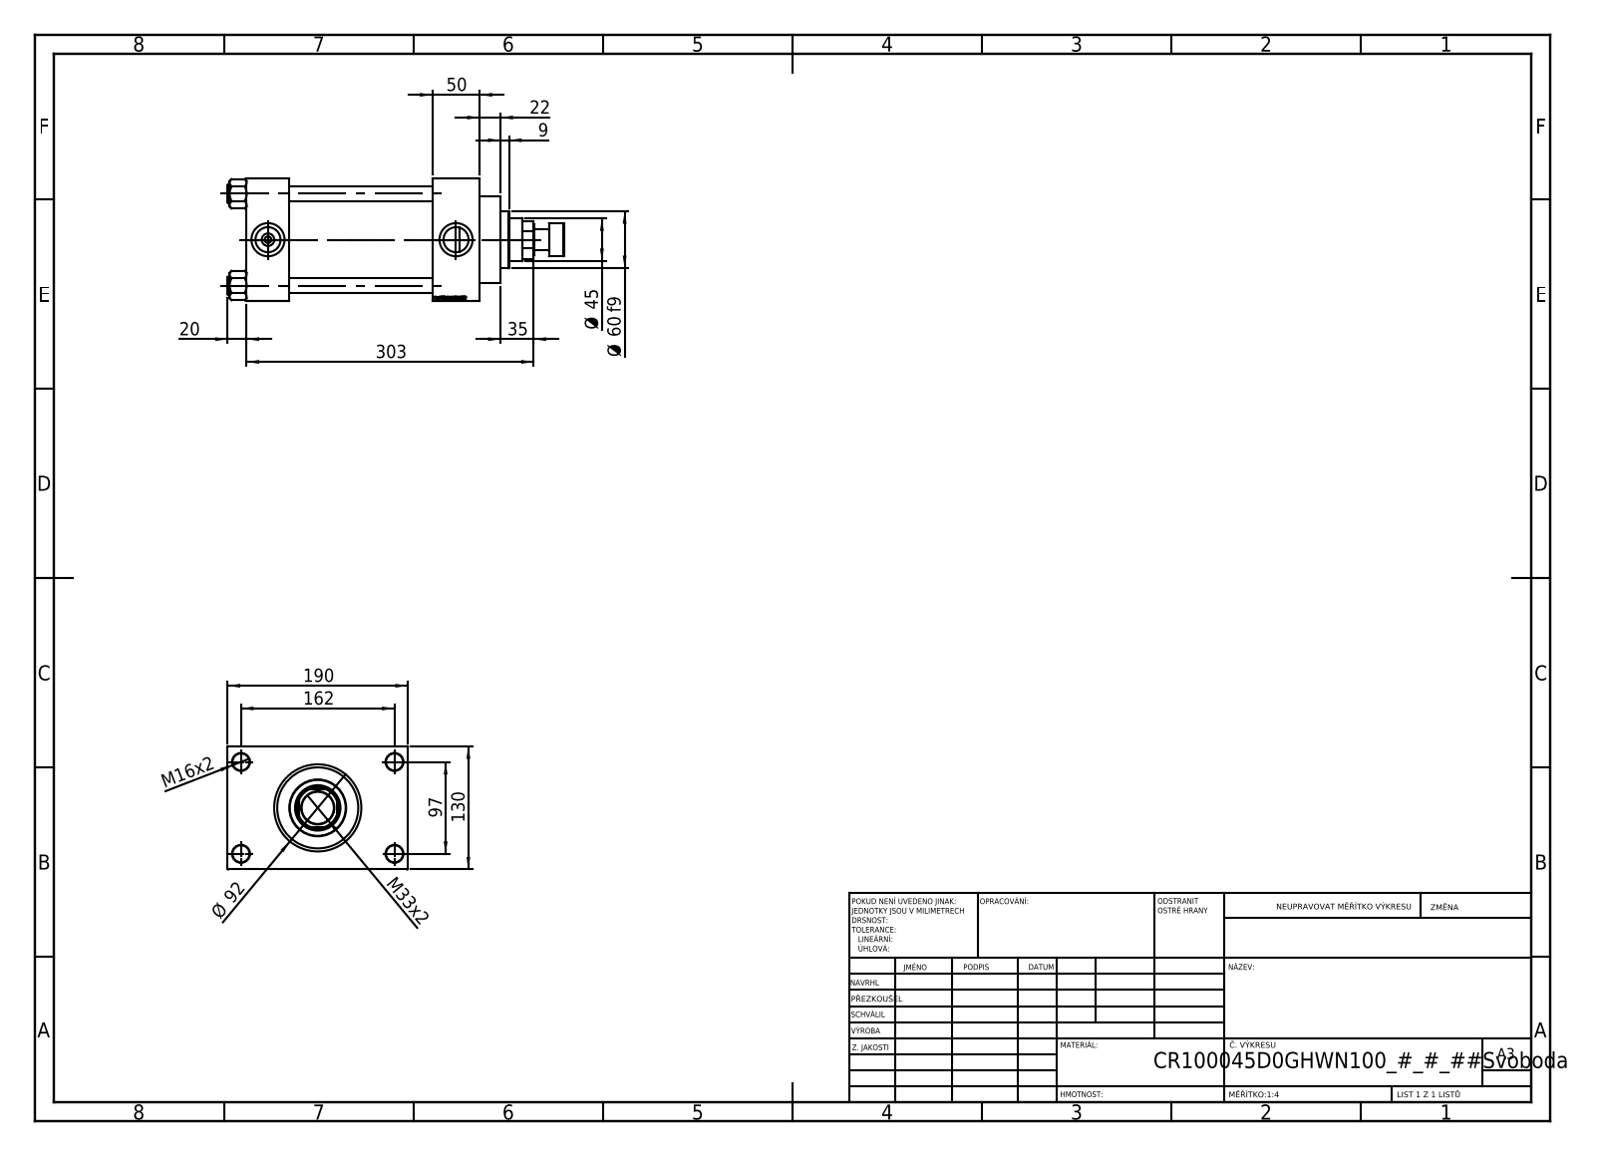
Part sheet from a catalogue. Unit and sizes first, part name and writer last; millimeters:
Units: millimetres
Overall size (bounding box): 355 × 190 × 130
Round holes (diameter × count): ⌀16 ×4, ⌀18 ×4, ⌀7 ×2, ⌀26.44 ×2, ⌀35 ×2, ⌀31.5 ×1, ⌀45 ×1, ⌀48 ×1, ⌀76 ×1, ⌀85.5 ×1, ⌀100 ×1
Round bosses / shafts (diameter × count): ⌀19 ×4, ⌀106 ×1, ⌀92 ×1, ⌀60 ×1, ⌀35 ×1, ⌀22 ×1
Partial cylindrical surfaces — rounded edges, fillets, slot ends (radius × count): R22 ×1
Main face-to-face distances: 130, 45, 196, 151, 246, 201, 50, 30, 160, 51
Hole centre spacings: 32.55, 68.52, 94.41, 96.9, 102.27, 129.45, 161.73, 97
Volume: 2 881 000 mm³ · Surface area: 439 830 mm²
Bodies: 12 solids, 1165 faces (549 planar, 92 cylindrical, 524 other)
Part name (STEP PRODUCT): V215CR_D_Body; V215CR_VCP_D; NUT_M5_D; V215CR_D_TYCINKA (+2 more)
STEP written by: SolidWorks 2019 (CONFIG_CONTROL_DESIGN)
